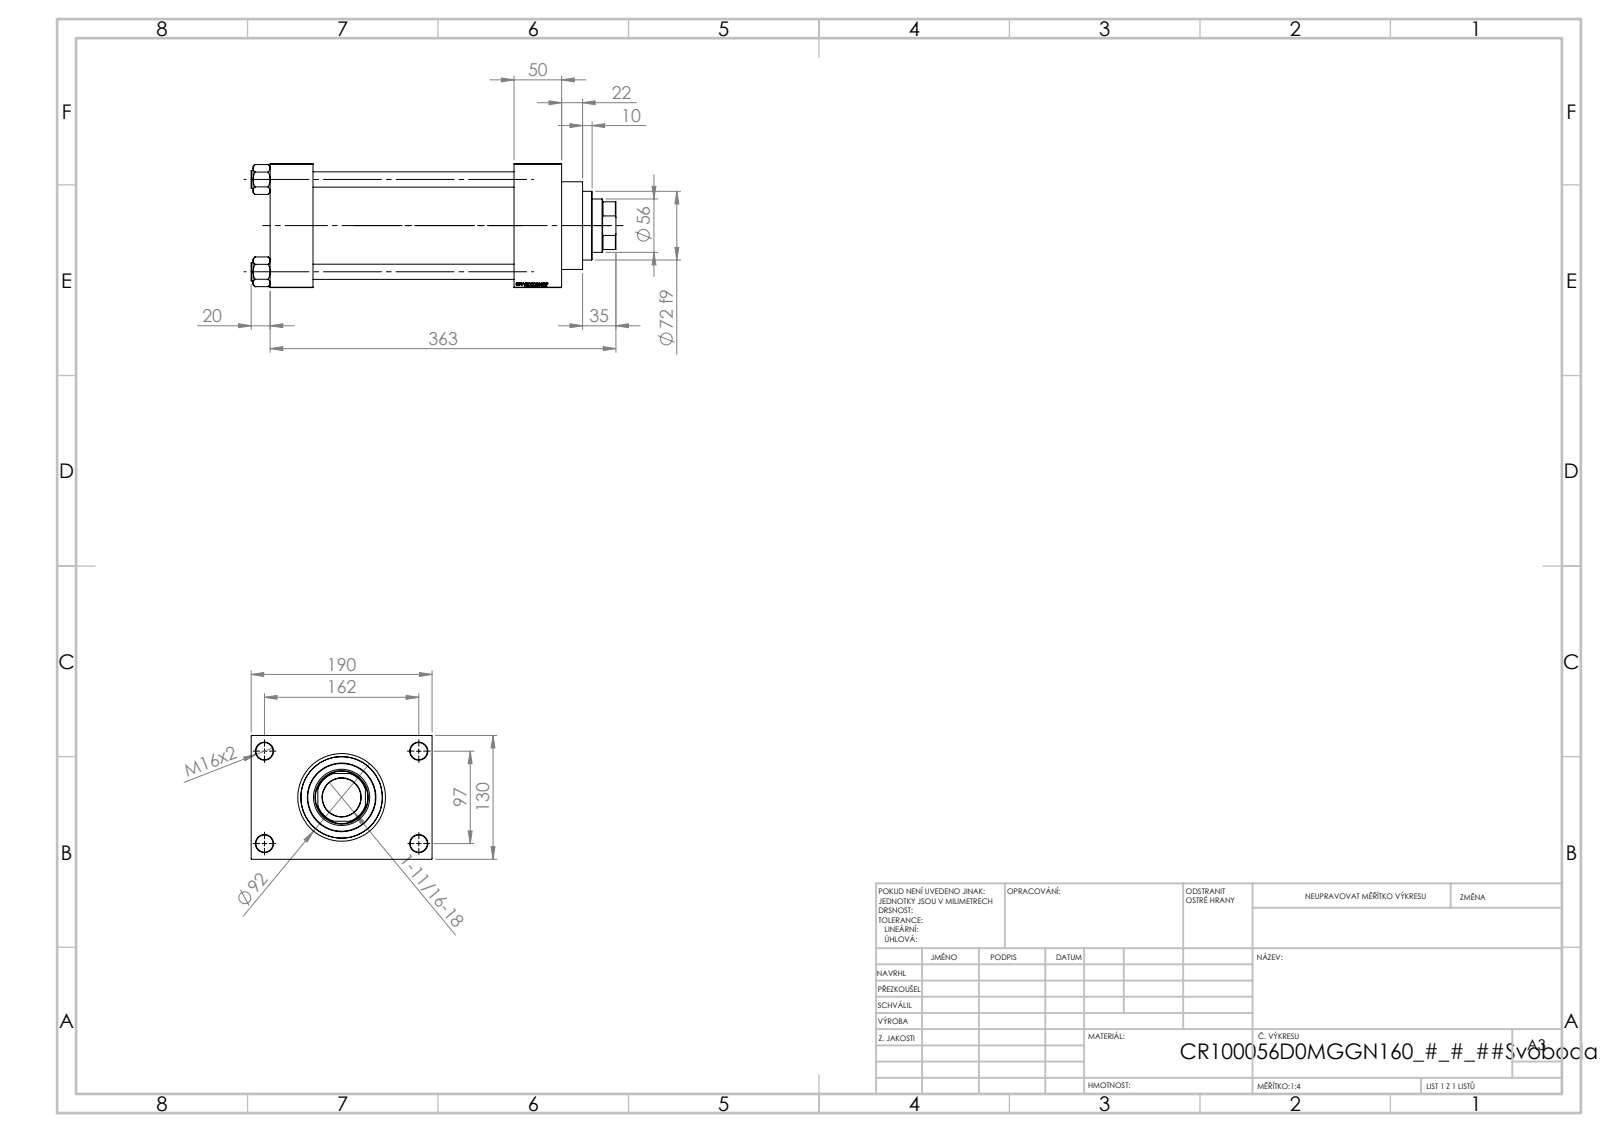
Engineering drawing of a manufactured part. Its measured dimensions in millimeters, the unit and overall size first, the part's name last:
Units: millimetres
Overall size (bounding box): 383 × 190 × 130
Round holes (diameter × count): ⌀16 ×4, ⌀18 ×4, ⌀7 ×2, ⌀26.44 ×2, ⌀35 ×2, ⌀40.5 ×1, ⌀56 ×1, ⌀59 ×1, ⌀76 ×1, ⌀85.5 ×1, ⌀100 ×1
Round bosses / shafts (diameter × count): ⌀19 ×4, ⌀106 ×1, ⌀92 ×1, ⌀72 ×1
Partial cylindrical surfaces — rounded edges, fillets, slot ends (radius × count): R27 ×1
Main face-to-face distances: 130, 50, 45, 256, 211, 160, 306, 261, 30, 190
Hole centre spacings: 32.55, 68.52, 94.41, 96.9, 102.27, 129.45, 161.73, 97
Volume: 3 238 000 mm³ · Surface area: 503 262 mm²
Bodies: 11 solids, 1152 faces (545 planar, 89 cylindrical, 518 other)
Part name (STEP PRODUCT): V215CR_D_Body; V215CR_D_TYCINKA; NUT_M5_D; V215_VC_A (+1 more)
STEP written by: SolidWorks 2019 (CONFIG_CONTROL_DESIGN)
